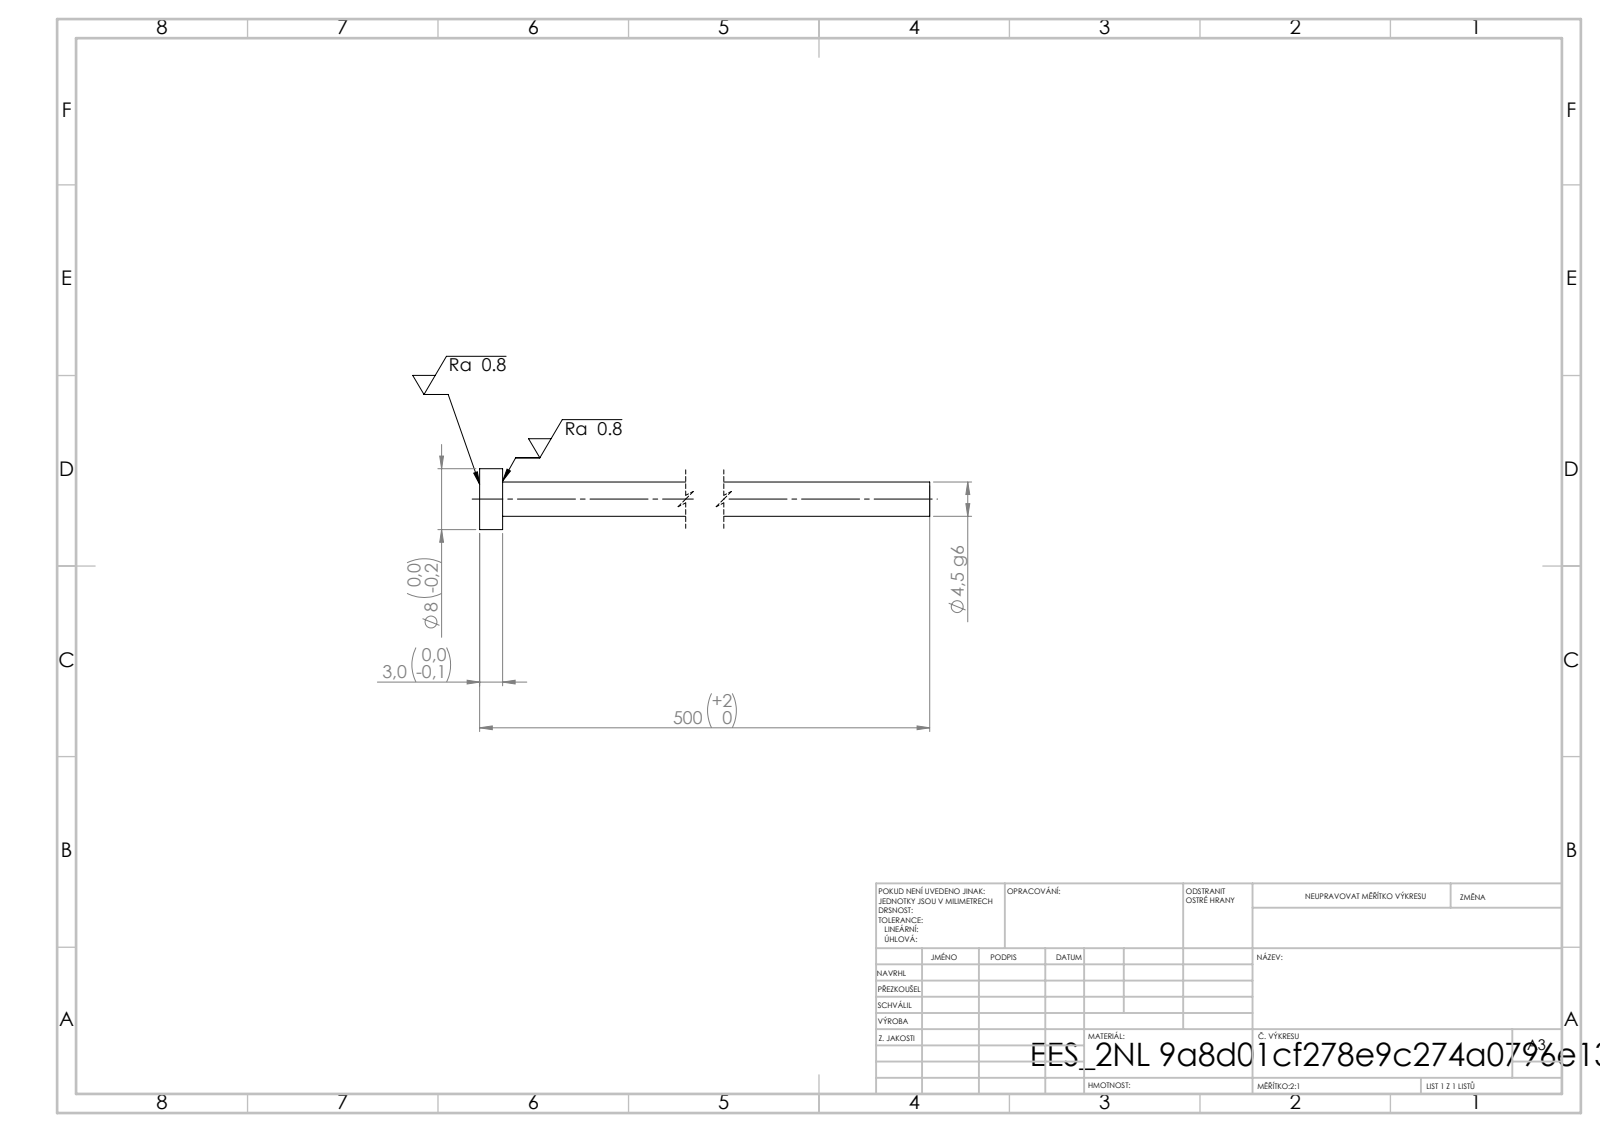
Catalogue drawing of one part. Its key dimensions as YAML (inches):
step_written_by: "SolidWorks 2019 (CONFIG_CONTROL_DESIGN)"
units: inches
bodies: {solids: 1, faces: 7, planar: 3, cylindrical: 4, other: 0}
overall_size: [19.685, 0.315, 0.315]
volume: 0.492
surface_area: 11.16
round_bosses_or_shafts:
  - {diameter: 0.315, count: 1}
  - {diameter: 0.177, count: 1}
face_to_face_distances: [0.118, 19.685, 19.567]
